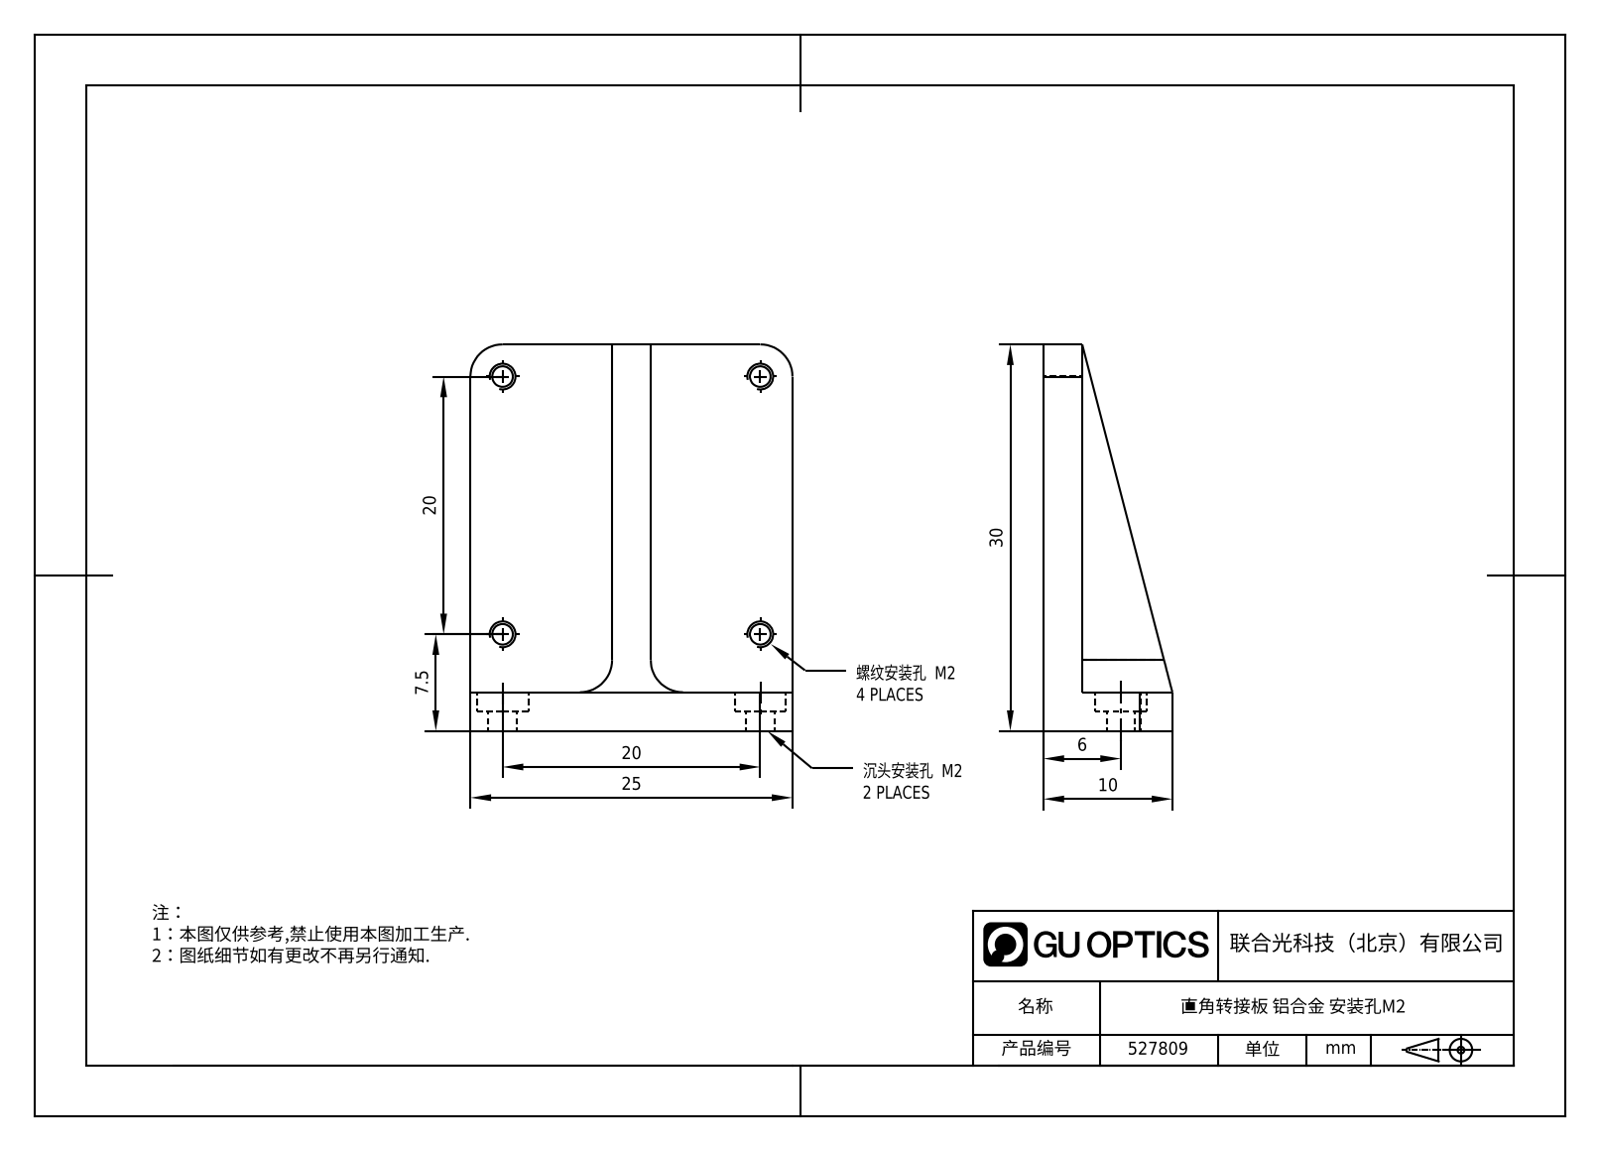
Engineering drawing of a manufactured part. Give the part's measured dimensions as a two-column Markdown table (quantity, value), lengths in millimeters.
| quantity | value |
| --- | --- |
| part name | 1.6.9.1_ZSJ-Z025_25mm直角转接板，带M2螺孔和M2沉头孔 |
| STEP written by | SolidWorks 2021 (CONFIG_CONTROL_DESIGN) |
| units | millimeters |
| bodies | 1 solid, 37 faces (15 planar, 22 cylindrical, 0 other) |
| overall size | 30 × 25 × 10 |
| volume | 2 988 mm³ |
| surface area | 2 441 mm² |
| round holes (diameter × count) | 1.6 × 4, 2.2 × 2, 4 × 2 |
| partial cylindrical surfaces (radius × count) | 2.5 × 6 |
| main face-to-face distances | 3, 11, 14, 25, 30, 27, 10, 7, 1.5, 28.5 |
| hole center spacings | 20, 28.28 |
